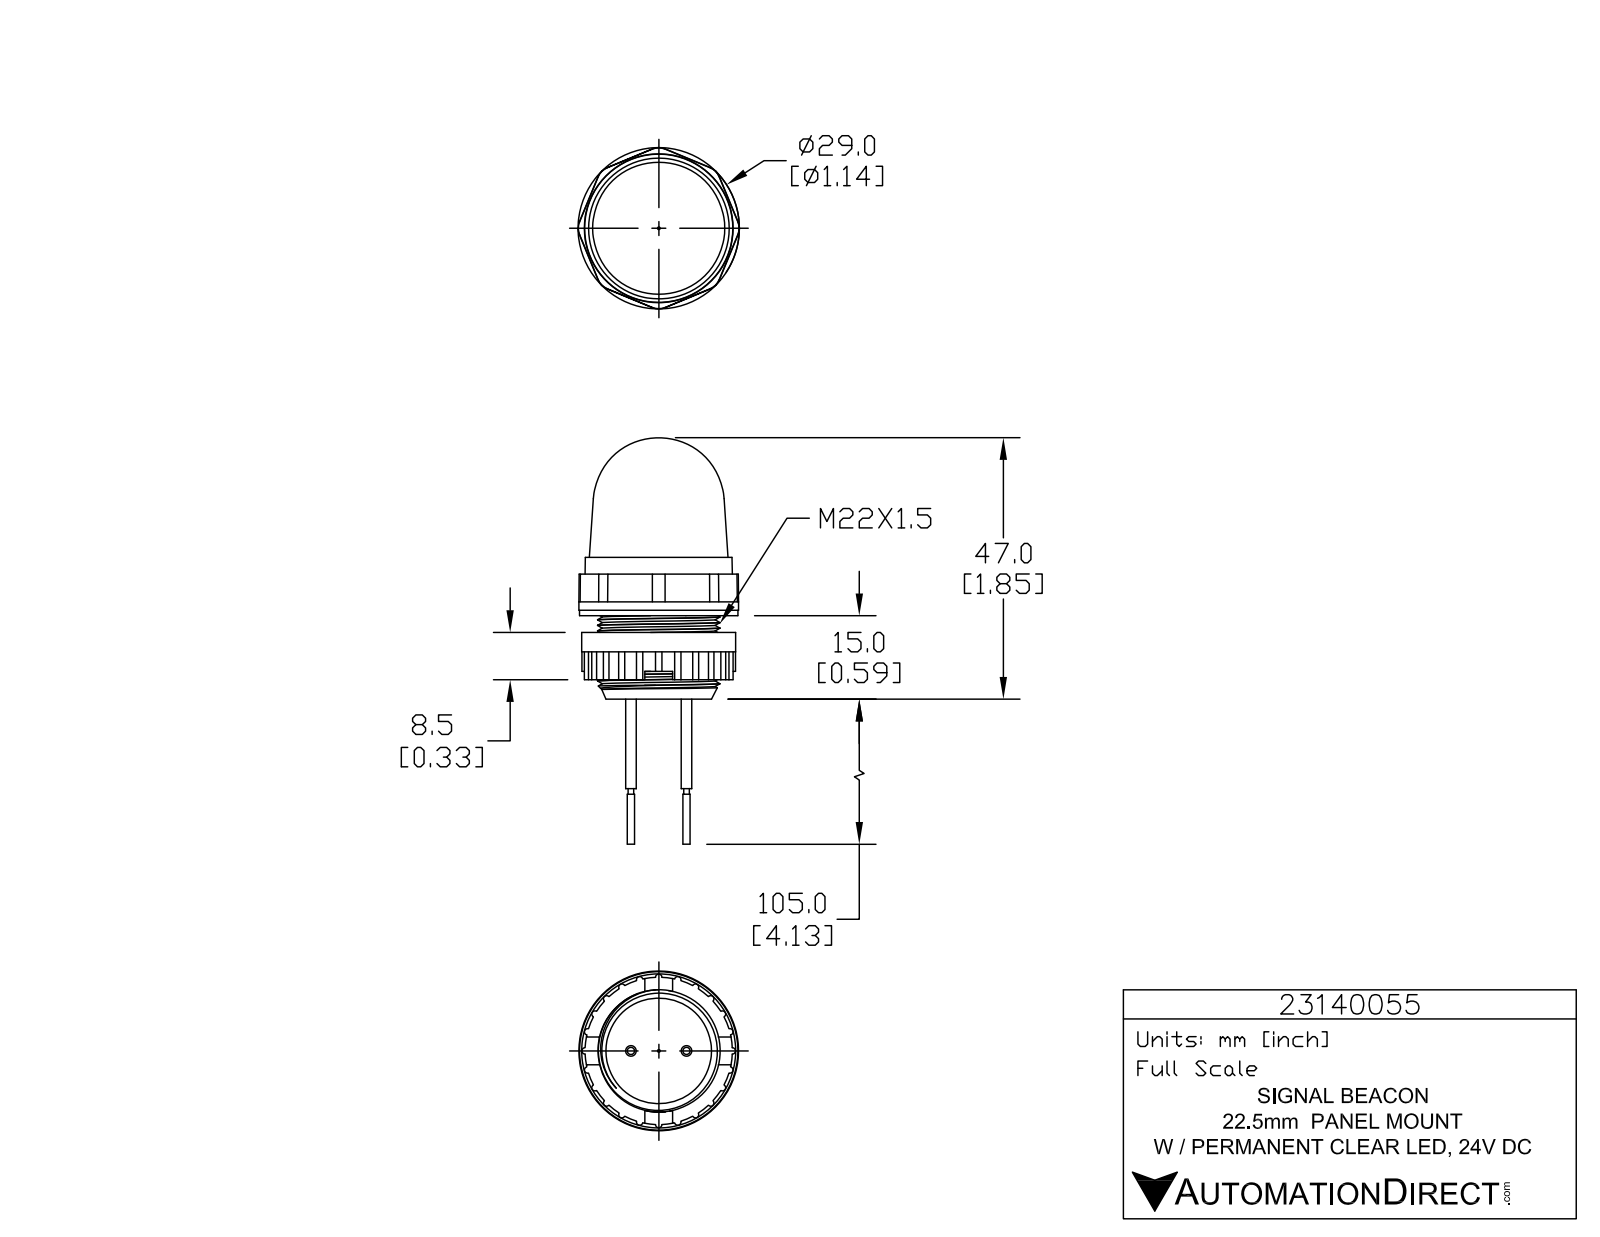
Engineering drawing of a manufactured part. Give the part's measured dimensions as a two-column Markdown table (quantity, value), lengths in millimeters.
| quantity | value |
| --- | --- |
| part name | 23140055 |
| STEP written by | SolidWorks 2017 (AUTOMOTIVE_DESIGN) |
| units | millimeters |
| bodies | 1 solid, 934 faces (568 planar, 269 cylindrical, 97 other) |
| overall size | 71.6 × 28.7 × 28.7 |
| volume | 20 570 mm³ |
| surface area | 7 845 mm² |
| round holes (diameter × count) | 0.5 × 3 |
| round bosses / shafts (diameter × count) | 2.9 × 3, 0.7 × 3, 1.9 × 2, 1.3 × 2, 1 × 2, 28.7 × 1, 28.5 × 1, 27.7 × 1 |
| partial cylindrical surfaces (radius × count) | 0.6 × 24, 3 × 8, 0.1 × 6, 0.1 × 6, 0.1 × 6, 1.7 × 6, 0.1 × 3, 0.2 × 3 |
| main face-to-face distances | 14, 3, 11, 2.5, 8.5, 11.5, 12.5, 10.5, 7.5, 5 |
